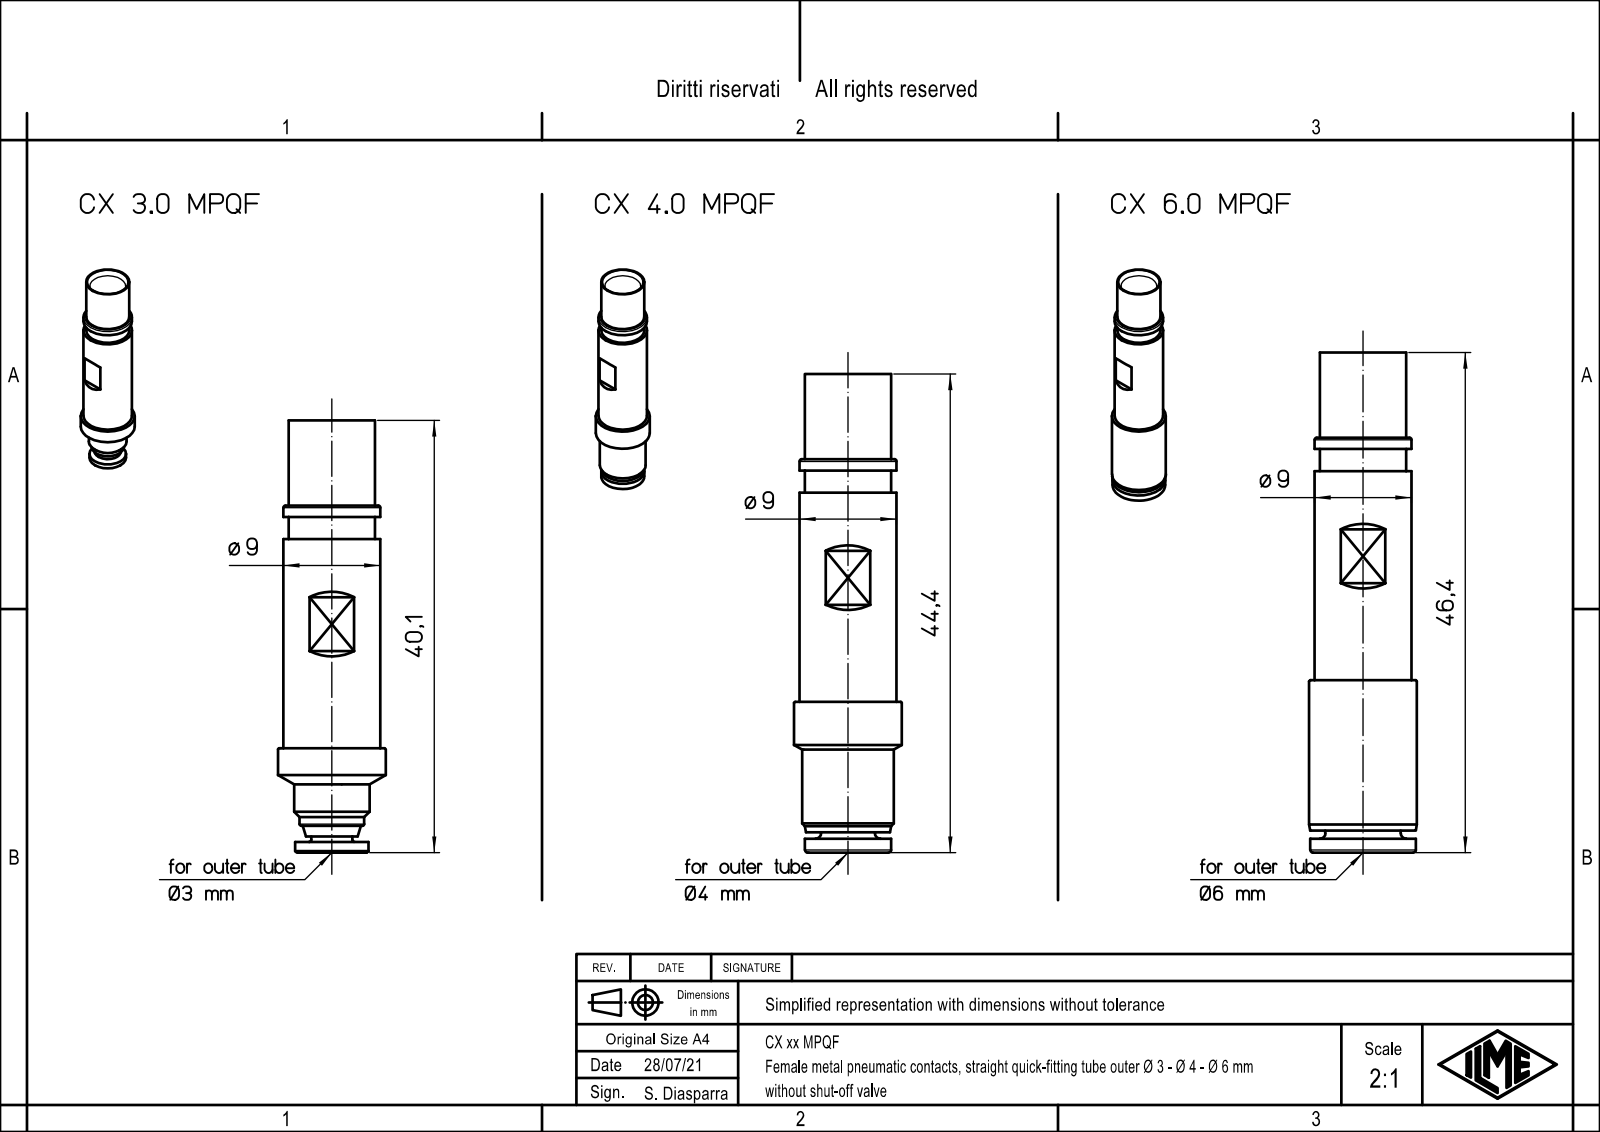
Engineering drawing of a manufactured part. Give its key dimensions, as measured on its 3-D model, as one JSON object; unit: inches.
{"part_name": "CX_3.0_MPQF", "step_written_by": "Creo Elements/Direct Modeling 20.1B 02-Apr-2019 (C) Parametric Technology GmbH (AUTOMOTIVE_DESIGN)", "units": "inches", "bodies": {"solids": 1, "faces": 73, "planar": 23, "cylindrical": 24, "other": 26}, "overall_size": [1.579, 0.394, 0.394], "volume_in3": 0.097, "surface_area_in2": 2.745, "round_holes": [[0.118, 1], [0.157, 1], [0.26, 1]], "round_bosses_or_shafts": [[0.394, 1], [0.354, 1], [0.315, 1], [0.276, 1], [0.268, 1], [0.236, 1], [0.15, 1]], "face_to_face_distances": [0.039, 0.315, 0.098, 0.382, 0.343, 1.226, 1.187, 0.844, 1.146, 1.106]}
